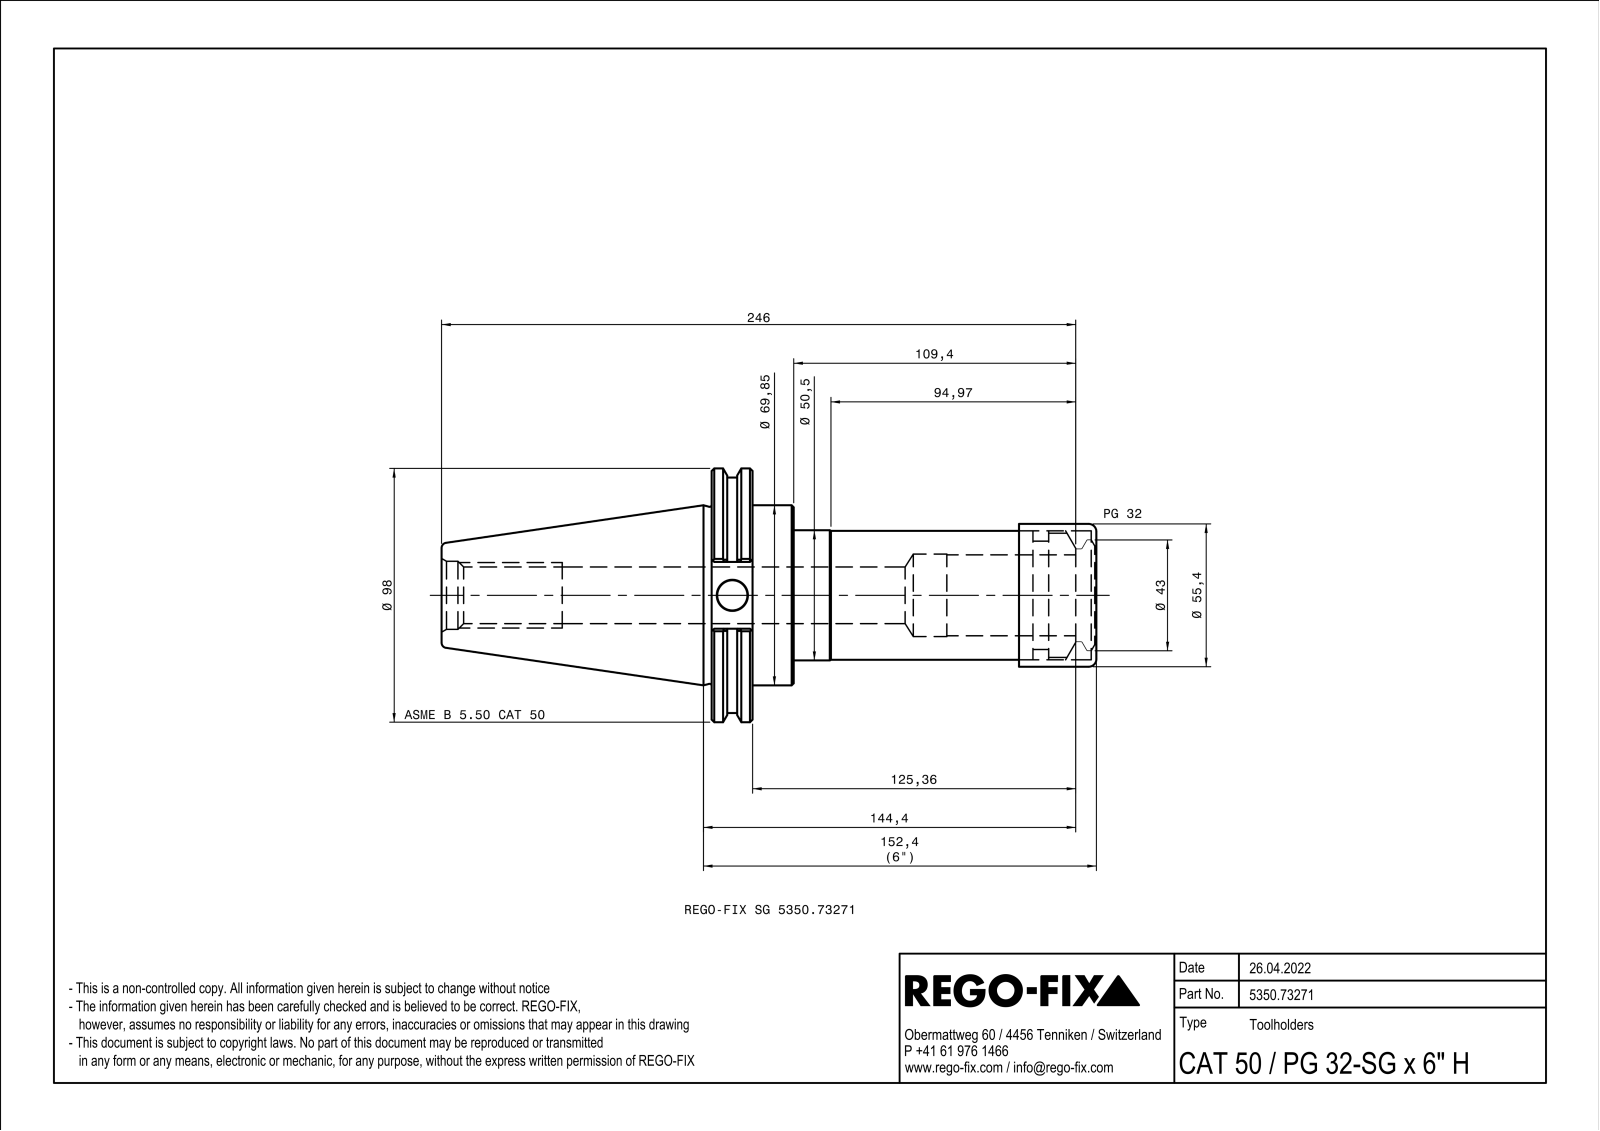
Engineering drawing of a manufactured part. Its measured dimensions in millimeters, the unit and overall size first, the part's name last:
Units: millimetres
Overall size (bounding box): 254 × 98.42 × 94.39
Round holes (diameter × count): ⌀11.7 ×1, ⌀21.96 ×1, ⌀26.4 ×1, ⌀33 ×1, ⌀38.25 ×1, ⌀48.38 ×1, ⌀50.05 ×1, ⌀51 ×1
Round bosses / shafts (diameter × count): ⌀98.42 ×1, ⌀91.3 ×1, ⌀69.85 ×1, ⌀55 ×1, ⌀50.5 ×1, ⌀50 ×1, ⌀42 ×1
Partial cylindrical surfaces — rounded edges, fillets, slot ends (radius × count): R0.5 ×12, R25.38 ×1, R27.12 ×1
Main face-to-face distances: 15.87, 15.96, 31.83, 117.4, 133.36, 149.23, 24.6, 92.8, 108.76, 124.63
Volume: 526 433 mm³ · Surface area: 84 978 mm²
Bodies: 1 solid, 123 faces (40 planar, 33 cylindrical, 50 other)
Part name (STEP PRODUCT): NOCUT
STEP written by: SIEMENS PLM Software Solid Edge ST10 (AUTOMOTIVE_DESIGN)
